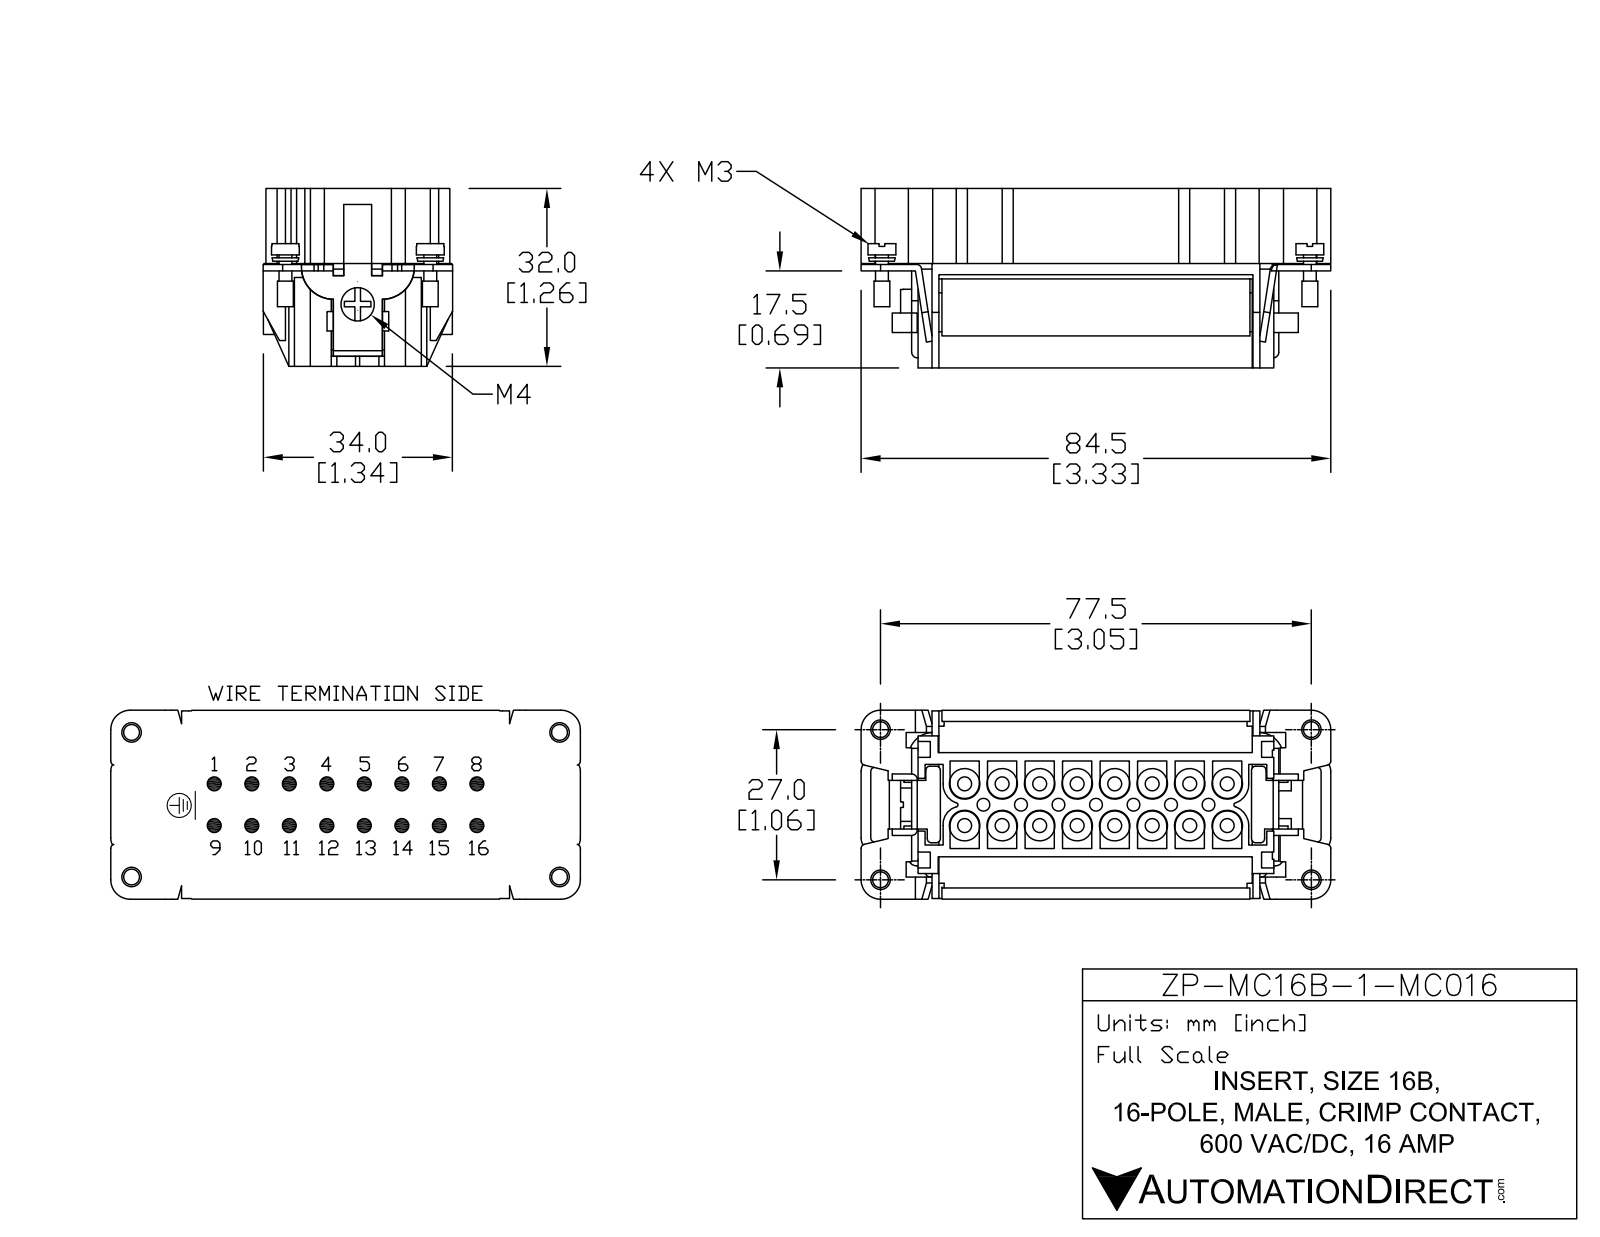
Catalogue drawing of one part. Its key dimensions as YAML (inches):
part_name: "ZP-MC16B-1-MC016"
step_written_by: "SolidWorks 2021 (CONFIG_CONTROL_DESIGN)"
units: inches
bodies: {solids: 1, faces: 1353, planar: 833, cylindrical: 250, other: 270}
overall_size: [3.346, 1.362, 1.311]
volume: 2.757
surface_area: 29.78
round_holes:
  - {diameter: 0.094, count: 7}
  - {diameter: 0.128, count: 1}
  - {diameter: 0.157, count: 1}
round_bosses_or_shafts:
  - {diameter: 0.181, count: 16}
  - {diameter: 0.213, count: 4}
  - {diameter: 0.205, count: 4}
  - {diameter: 0.118, count: 4}
  - {diameter: 0.091, count: 4}
  - {diameter: 0.276, count: 1}
  - {diameter: 0.142, count: 1}
partial_cylinders:
  - {radius: 0.02, count: 44}
  - {radius: 0.112, count: 16}
  - {radius: 0.012, count: 14}
  - {radius: 0.039, count: 12}
  - {radius: 0.079, count: 12}
  - {radius: 0.059, count: 8}
  - {radius: 0.047, count: 4}
  - {radius: 0.055, count: 4}
face_to_face_distances: [0.047, 1.272, 0.039, 0.037, 0.689, 0.699, 0.736, 1.362, 0.728, 0.738]
hole_center_spacings: [0.264, 0.528, 0.791, 1.055, 1.319, 1.583]
